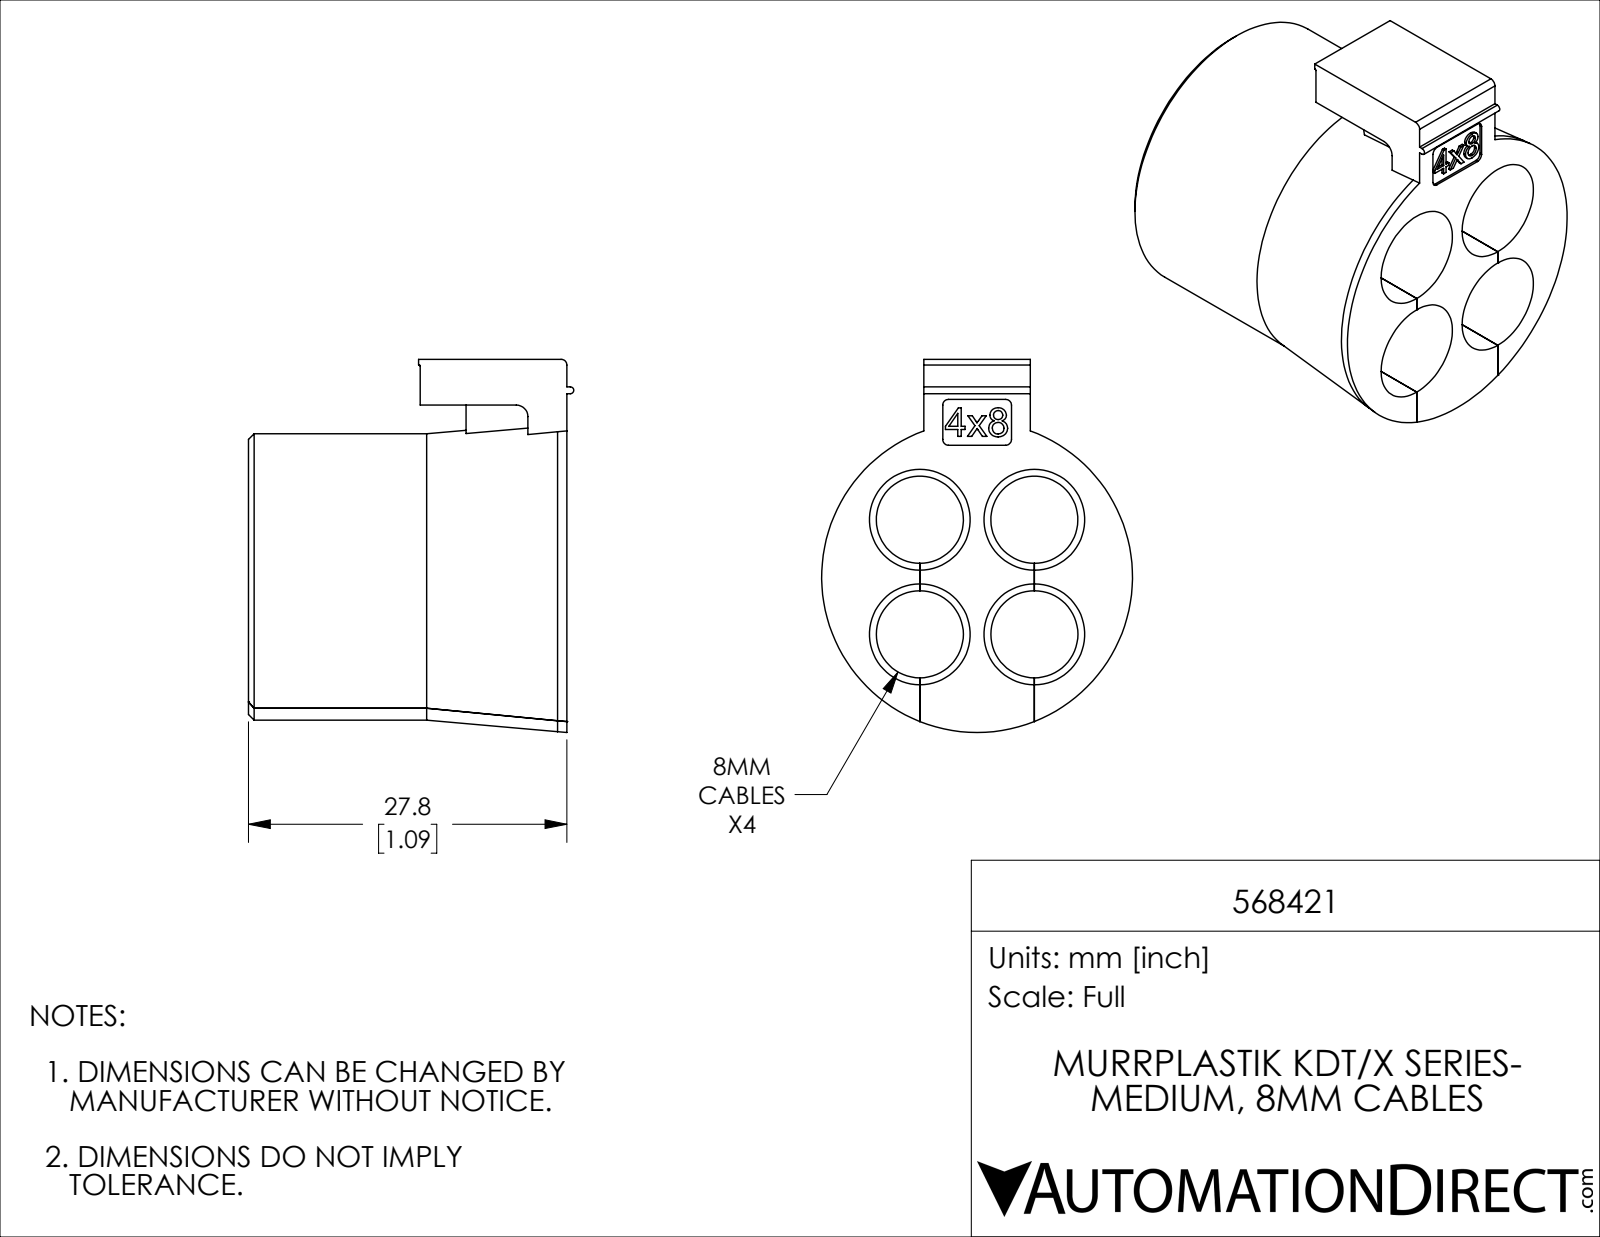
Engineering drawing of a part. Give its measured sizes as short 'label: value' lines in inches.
name: 568421
written by: SolidWorks 2019 (CONFIG_CONTROL_DESIGN)
unit: in
bodies: 1 solid, 165 faces (63 planar, 50 cylindrical, 52 other)
size: 1.282 × 1.118 × 1.069
volume: 0.491 in³; area: 10.39 in²
holes: 4× ⌀0.299, 4× ⌀0.346
bosses: 1× ⌀0.984
rounds: 5× R0.02, 1× R0.004, 1× R0.012, 1× R0.039
face distances: 1.094, 0.393, 0.013, 0.014, 0.38, 0.38, 0.393, 0.394, 0.157, 0.366
hole spacings: 0.394, 0.557
